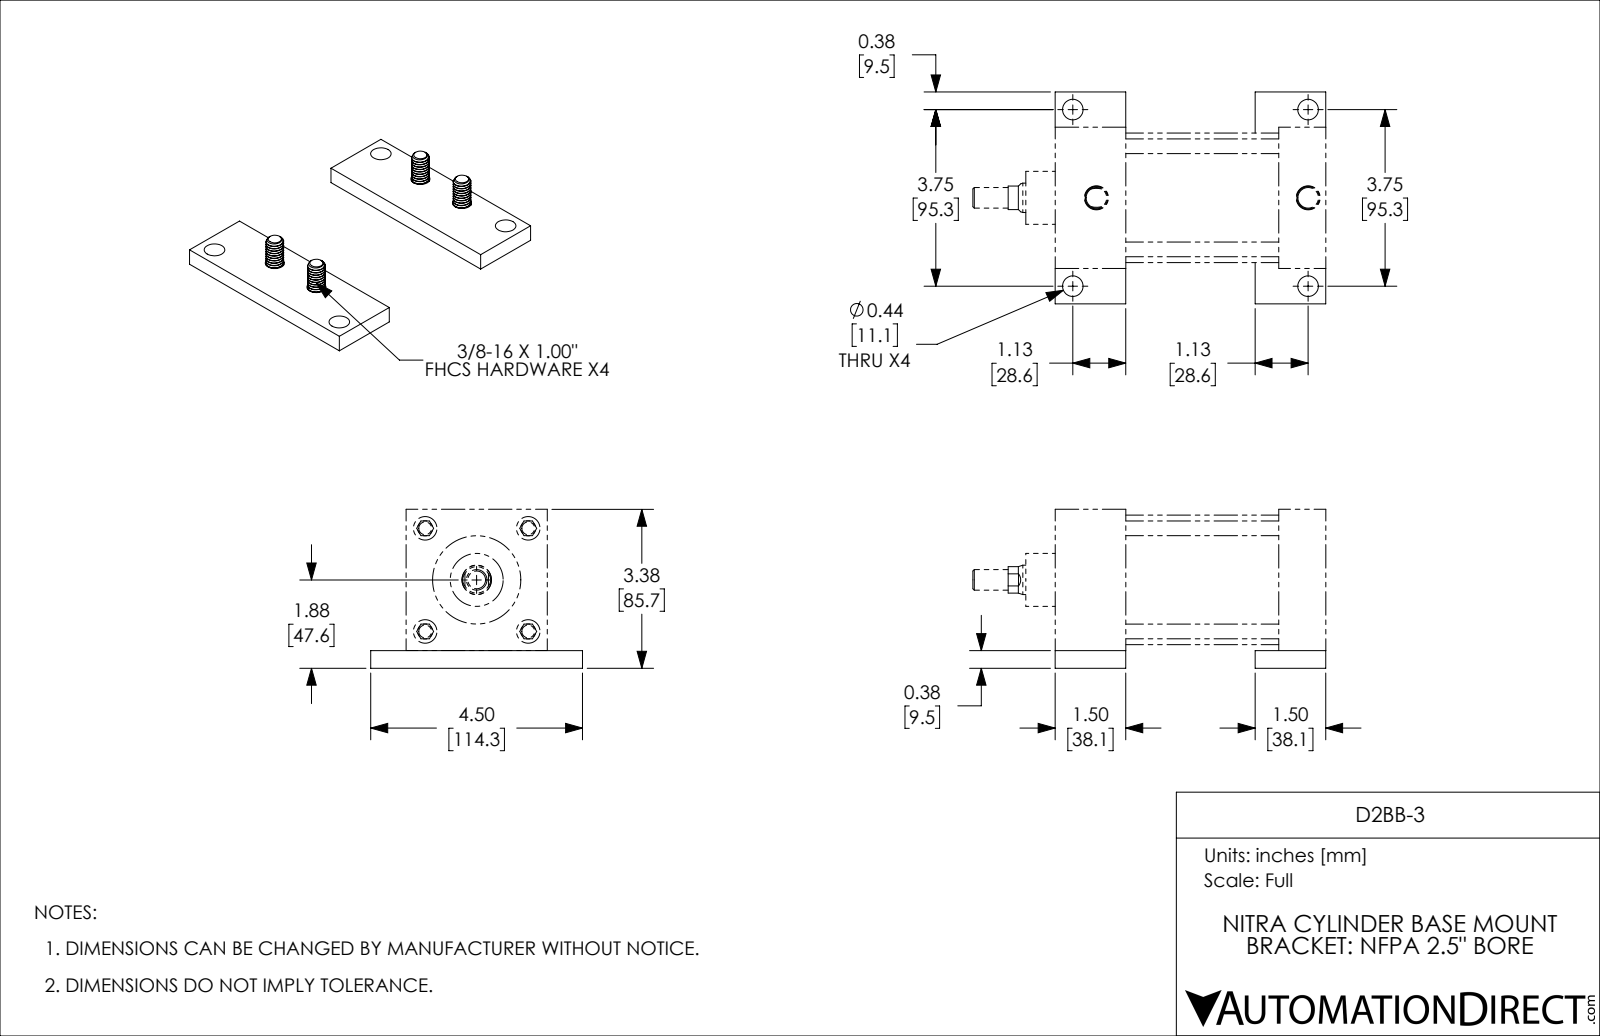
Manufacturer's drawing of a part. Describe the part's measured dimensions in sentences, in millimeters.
The part is named "D2BB-3_2; D2BB-3_1; D2BB-3". Its 3-D file was written by "SolidWorks 2019 (CONFIG_CONTROL_DESIGN)". It is 6 solids with 344 faces: 48 planar, 212 cylindrical and 84 other. Overall it measures 146 by 114.3 by 25.4 millimeters. Its volume is 82 380 cubic millimeters and its surface area 30 850 square millimeters. Round holes: 4 of diameter 10.3, 4 of diameter 11.1. Round bosses or shafts: 4 of diameter 19.8, 4 of diameter 9.5, 4 of diameter 7.5. The main face-to-face distances are 9.5, 38.1, 108, 146.1, 69.9, 114.3, 15.9, 25.4, 4.2, 5.4. The hole center spacings are 31.8, 34.8, 65.1, 111.1, 115.6, 127, 129.4, 140.6.
